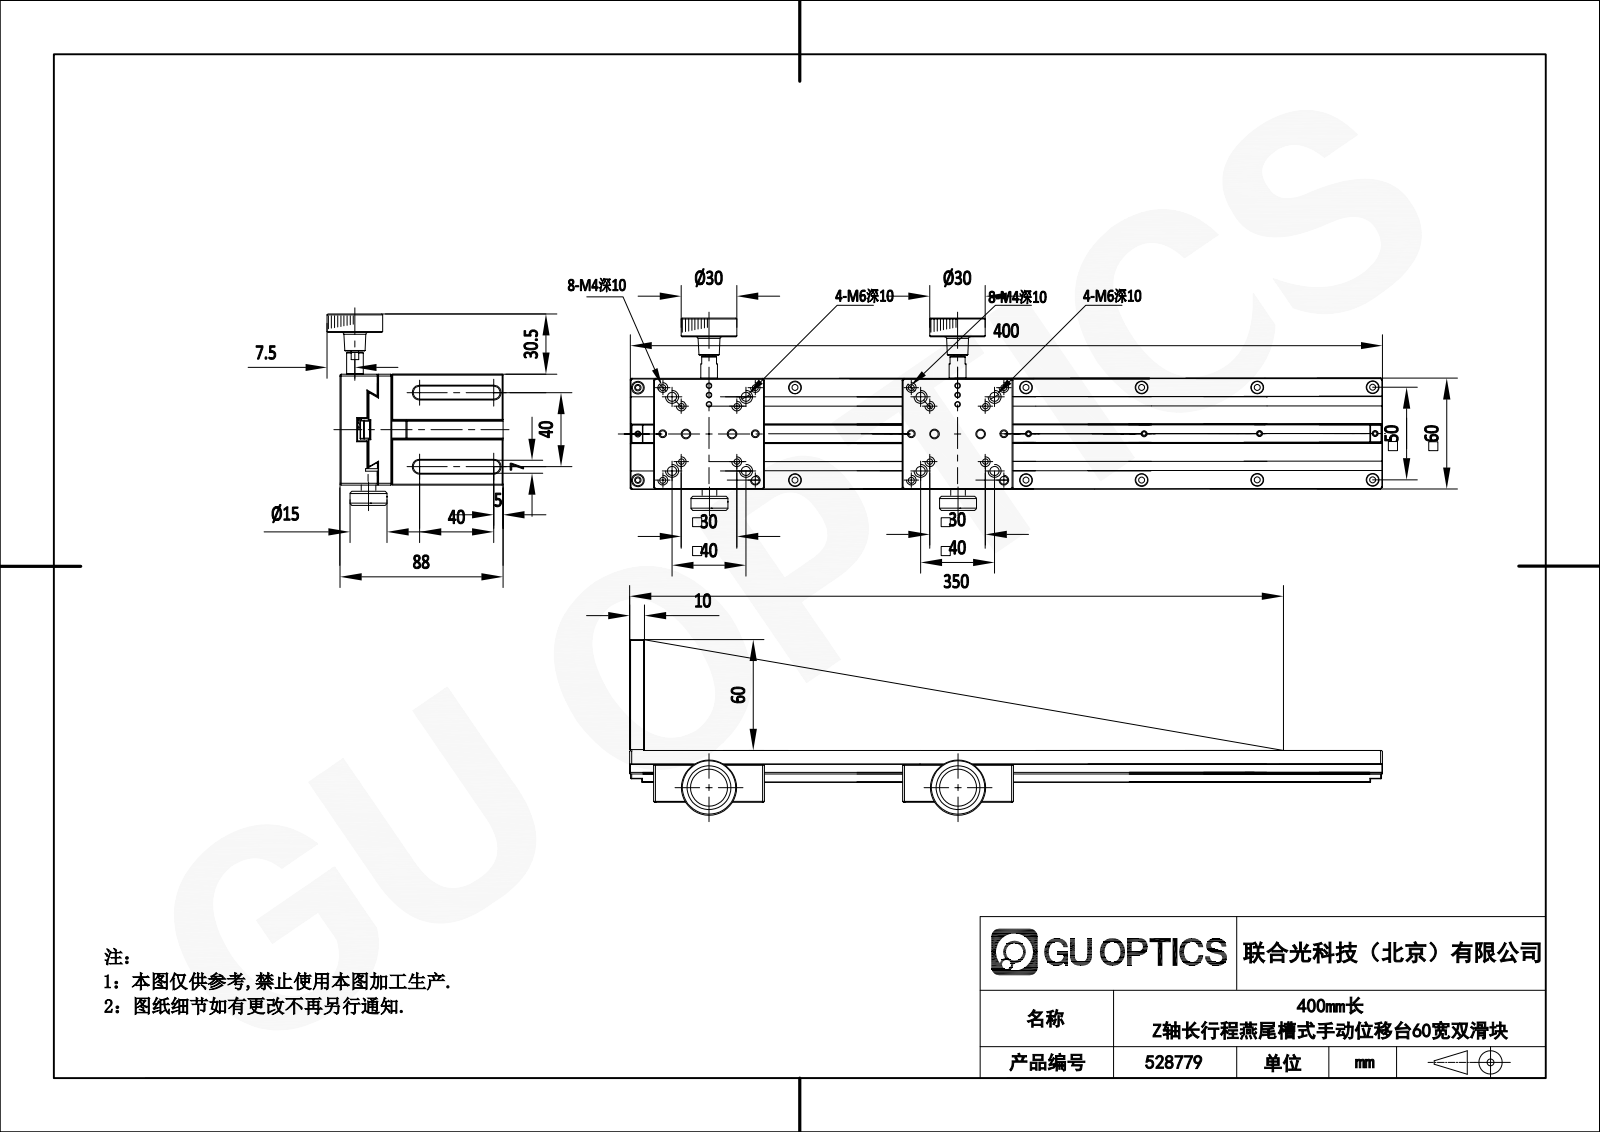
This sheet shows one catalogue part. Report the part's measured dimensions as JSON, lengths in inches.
{"part_name": "528779", "step_written_by": "SolidWorks 2020 (CONFIG_CONTROL_DESIGN)", "units": "inches", "bodies": {"solids": 59, "faces": 1693, "planar": 885, "cylindrical": 357, "other": 451}, "overall_size": [16.063, 4.026, 2.562], "volume_in3": 43.89, "surface_area_in2": 324.2, "round_holes": [[0.13, 34], [0.177, 26], [0.098, 20], [0.197, 14], [0.236, 12], [0.315, 10], [0.081, 6], [0.114, 6], [0.157, 2], [0.161, 2], [0.394, 2]], "round_bosses_or_shafts": [[0.118, 22], [0.217, 12], [0.157, 8], [0.177, 6], [0.098, 6], [0.354, 4], [0.276, 4], [1.181, 2]], "partial_cylinders_radius": [[0.041, 2]], "face_to_face_distances": [0.394, 0.874, 0.48, 0.945, 1.417, 2.362, 0.689, 0.295, 0.185, 0.315], "hole_center_spacings": [1.969, 2.65, 5.502, 2.953, 0.278, 1.1, 1.392, 1.623]}
